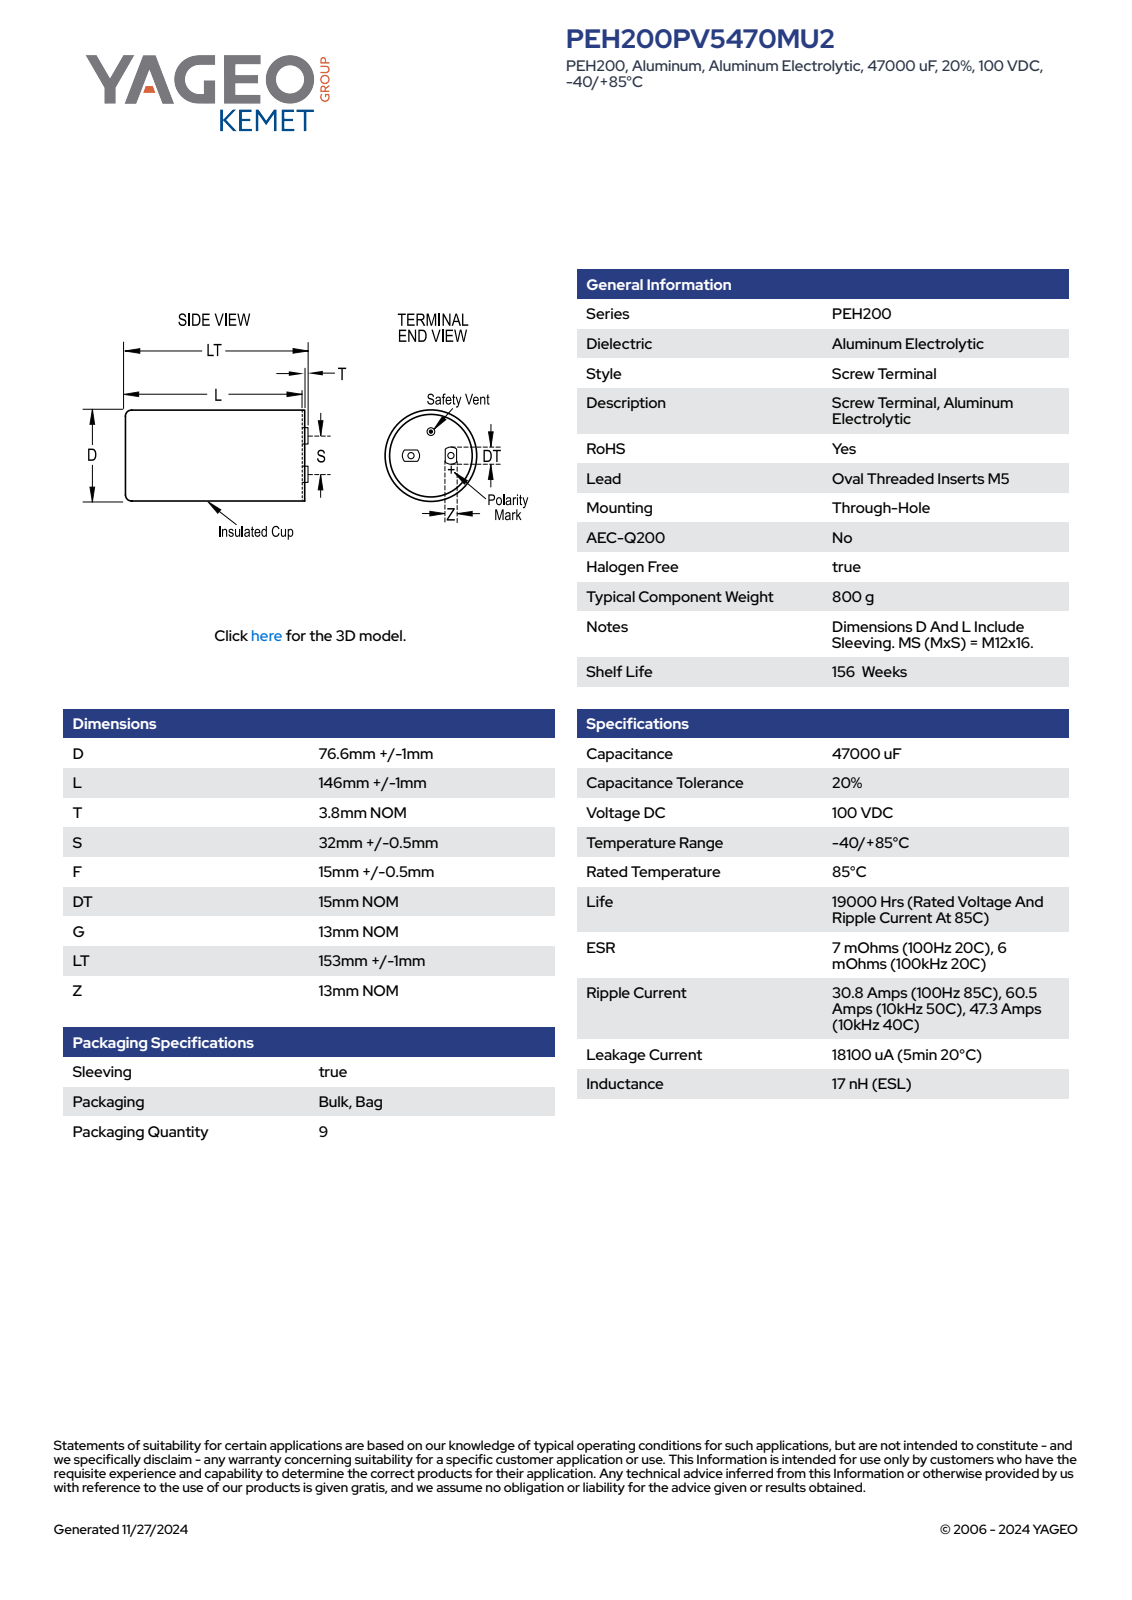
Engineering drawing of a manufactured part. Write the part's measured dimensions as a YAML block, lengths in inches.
part_name: "Oval_Terminal_6; CARC_D77.6L147S32T3.8; Can_6"
step_written_by: "SolidWorks 2014 (AUTOMOTIVE_DESIGN)"
units: inches
bodies: {solids: 3, faces: 91, planar: 38, cylindrical: 21, other: 32}
overall_size: [6.063, 3.055, 3.055]
volume: 42.58
surface_area: 74.7
round_holes:
  - {diameter: 0.158, count: 2}
  - {diameter: 2.976, count: 1}
round_bosses_or_shafts:
  - {diameter: 0.295, count: 2}
  - {diameter: 3.055, count: 1}
partial_cylinders:
  - {radius: 0.295, count: 2}
  - {radius: 1.527, count: 1}
face_to_face_distances: [5.787, 0.276, 6.063, 0.15, 0.126, 5.913, 0.512, 0.197, 0.472, 0.323]
hole_center_spacings: [0.63, 1.26]
